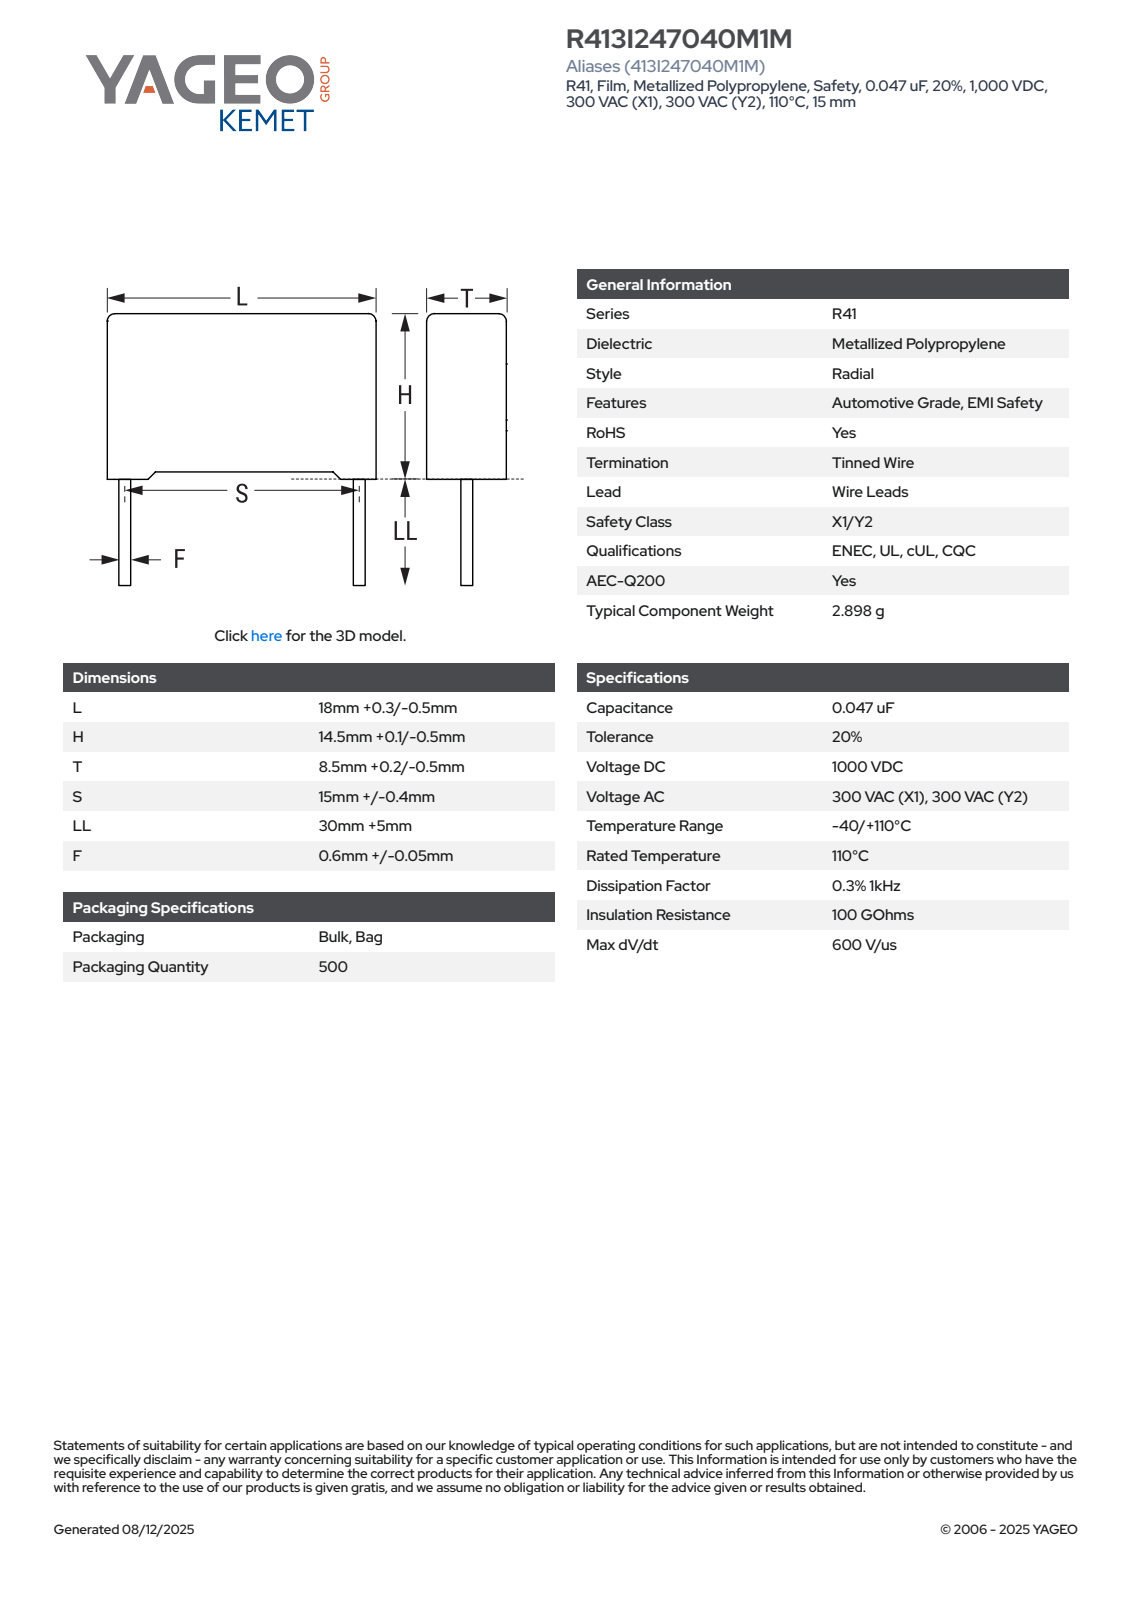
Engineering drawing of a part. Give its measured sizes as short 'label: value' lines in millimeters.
name: CFR_RB2_18X14.5X8.5_L18.3H14.6T8.7S15LL35F0.65
written by: SolidWorks 2021 (AUTOMOTIVE_DESIGN)
unit: mm
bodies: 4 solids, 85 faces (77 planar, 8 cylindrical, 0 other)
size: 49.6 × 18.3 × 8.71
volume: 2 243 mm³; area: 1 281 mm²
bosses: 2× ⌀0.65
rounds: 4× R0.5
face distances: 8.7, 13.85, 18.3, 0.61, 0.75, 14.6, 8.09, 0.5, 14.1, 17.69
